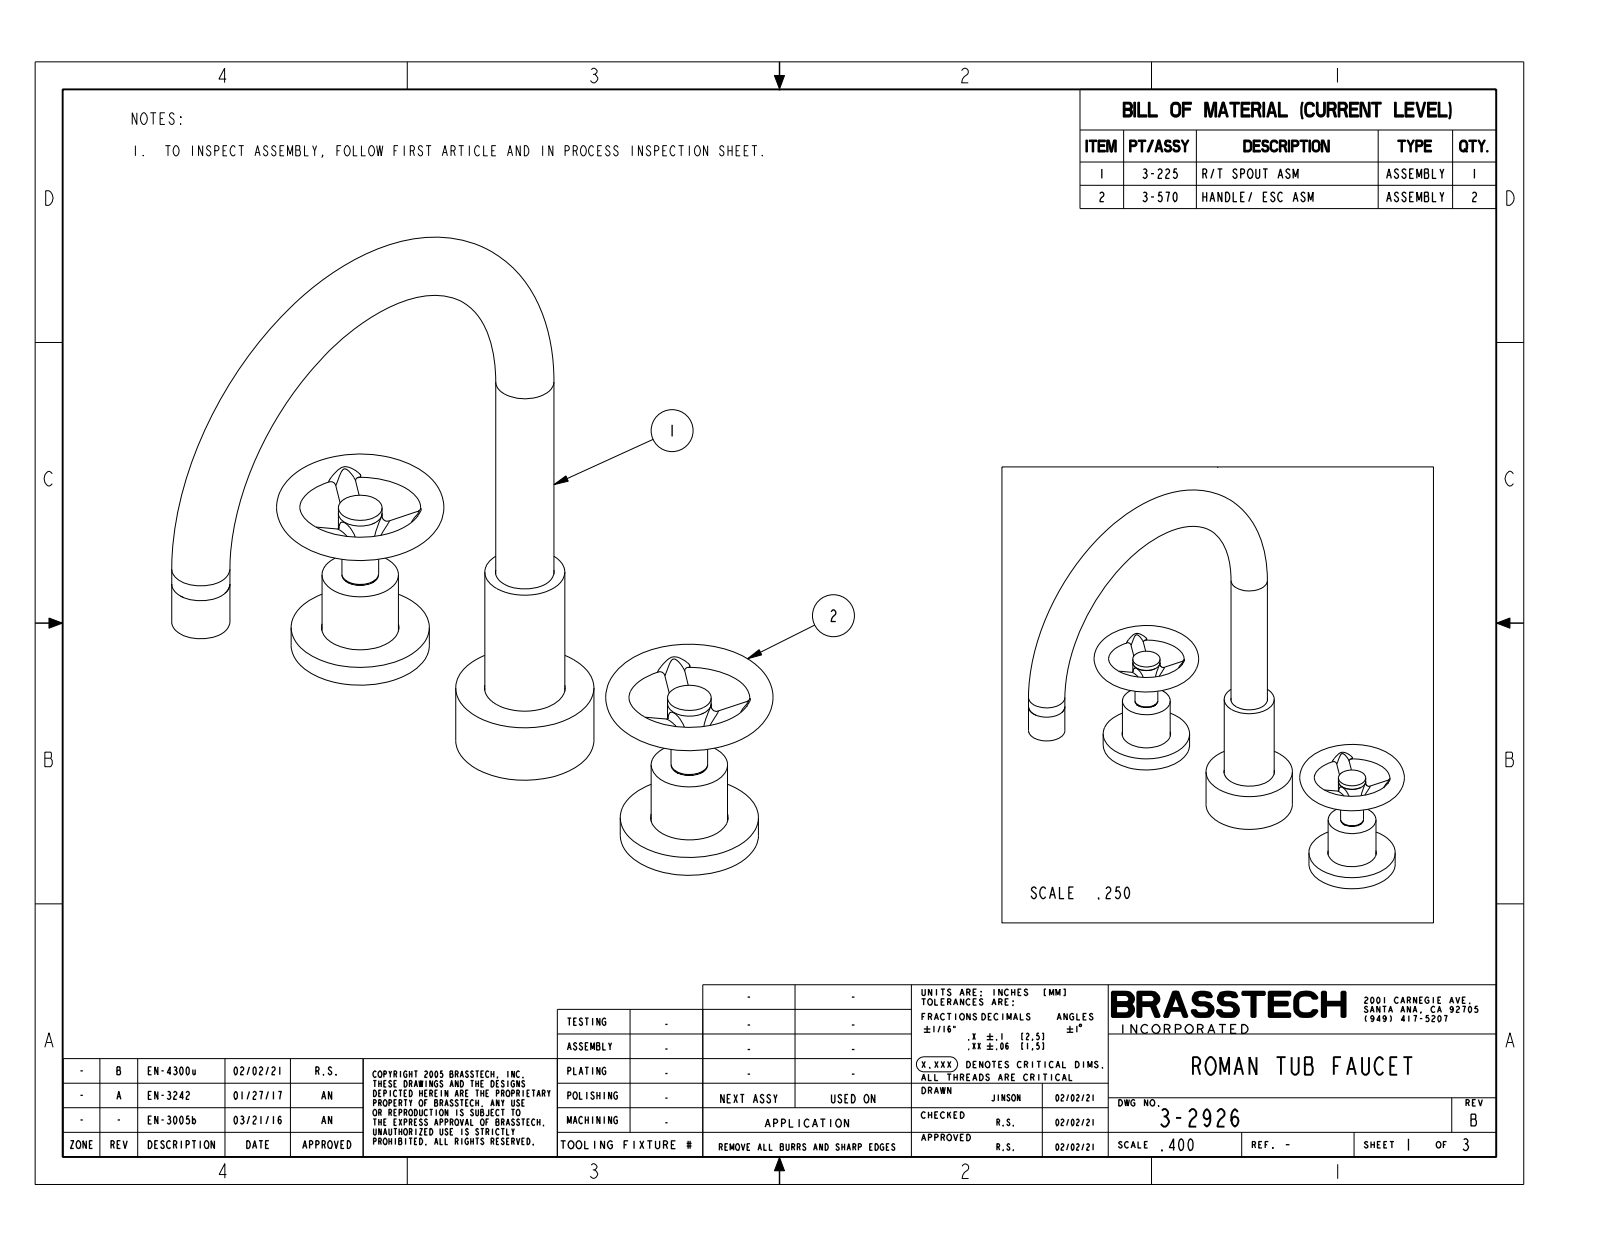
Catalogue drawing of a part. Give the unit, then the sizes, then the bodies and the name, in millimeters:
Units: millimetres
Overall size (bounding box): 304.2 × 276.2 × 249.3
Round bosses / shafts (diameter × count): ⌀8.9 ×6, ⌀60.3 ×3, ⌀33.4 ×2, ⌀25.4 ×2, ⌀19.1 ×2, ⌀16 ×2, ⌀10.2 ×2, ⌀34.9 ×1
Main face-to-face distances: 9.5, 28, 18.5, 37.7, 28.1, 9.7, 73.5, 64, 45.5, 35.8
Volume: 525 700 mm³ · Surface area: 94 190 mm²
Bodies: 3 solids, 102 faces (16 planar, 40 cylindrical, 46 other)
Part name (STEP PRODUCT): 3-2926
STEP written by: CREO PARAMETRIC BY PTC INC, 2018400 (CONFIG_CONTROL_DESIGN)
